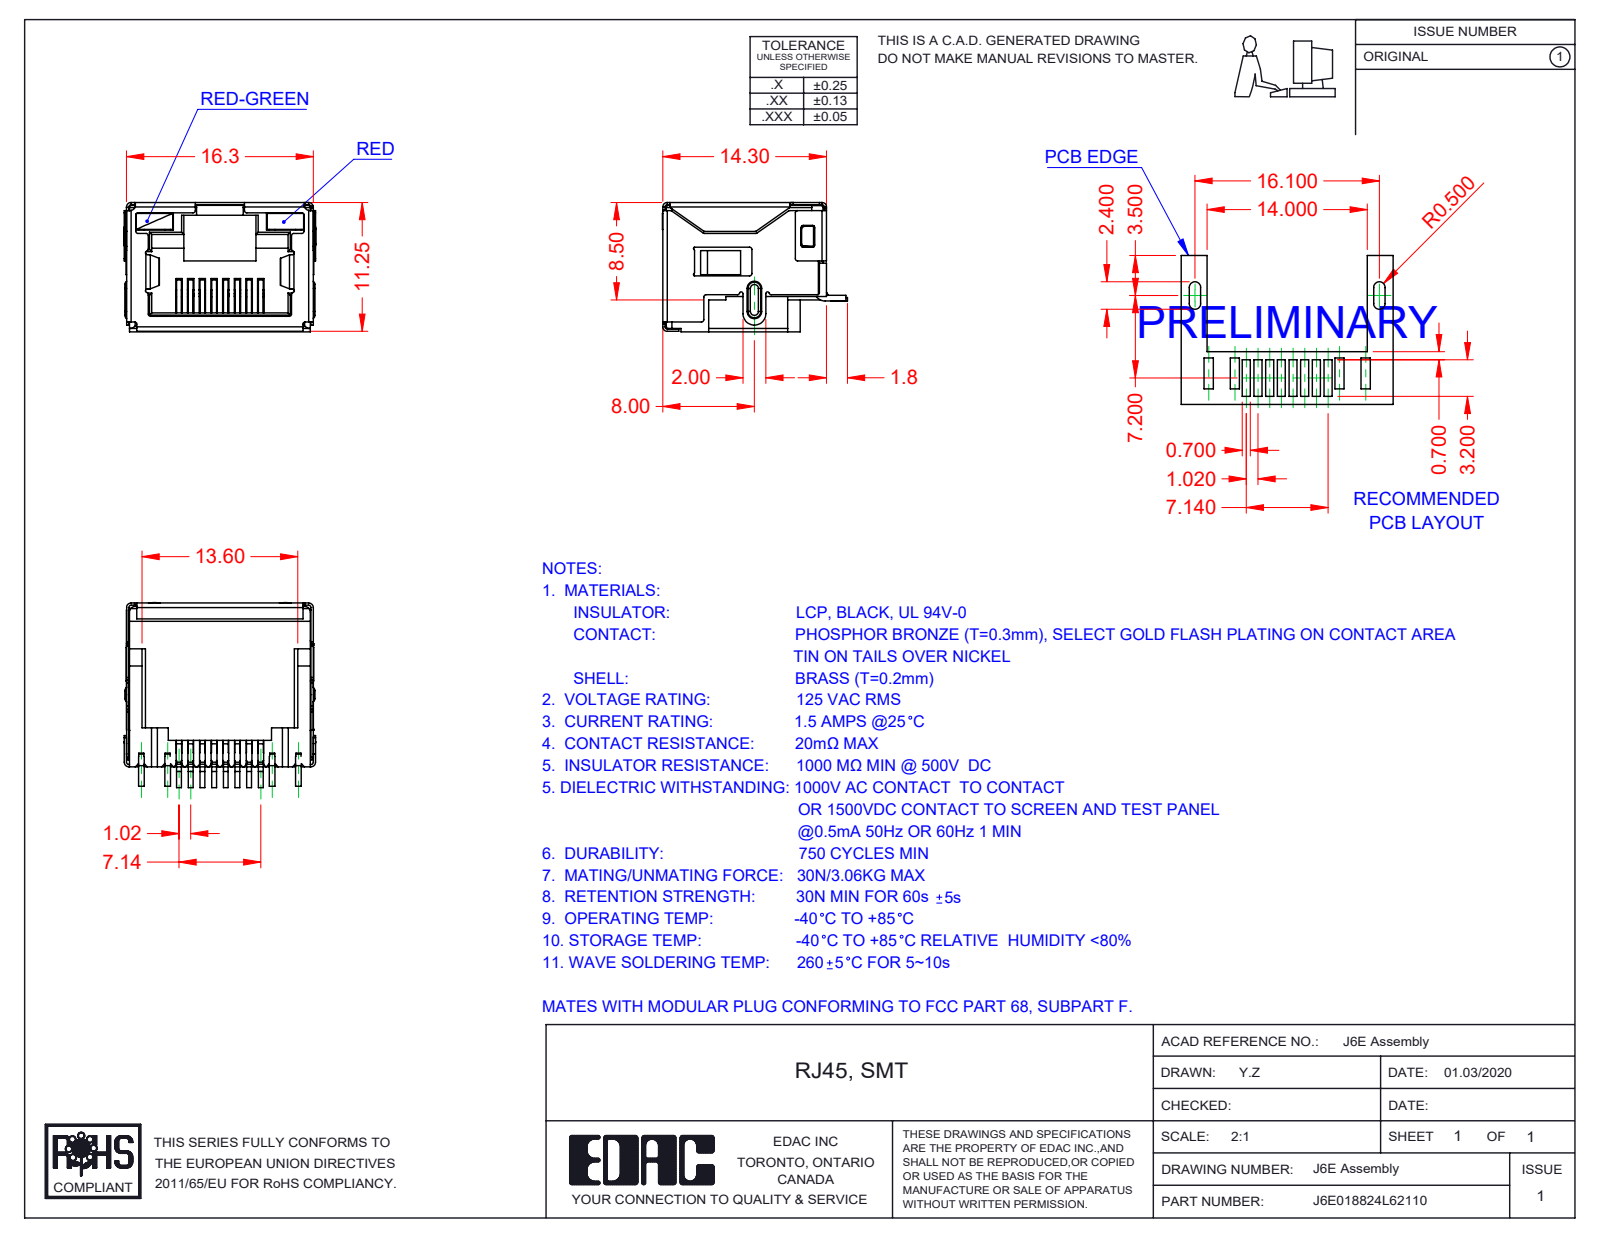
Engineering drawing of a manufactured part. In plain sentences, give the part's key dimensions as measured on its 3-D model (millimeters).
The part is named "6E Shield_LED; J6E018824L62110; 6E Contacts; 6E Insulator_LED (+2 more)". Its 3-D file was written by "SolidWorks 2016 (CONFIG_CONTROL_DESIGN)". It is 12 solids with 1498 faces: 1099 planar, 349 cylindrical and 50 other. Overall it measures 16.75 by 16.15 by 11.3 millimeters. Its volume is 1 109 cubic millimeters and its surface area 4 045 square millimeters. Partial cylindrical surfaces (rounded edges, fillets, slot ends): 82 of radius 0.2, 17 of radius 0.25, 13 of radius 0.4, 13 of radius 0.5, 10 of radius 0.1, 7 of radius 0.15, 4 of radius 0.3, 3 of radius 1. The main face-to-face distances are 11.05, 16.05, 16.1, 15.85, 11.1, 11.3, 2.4, 0.7, 9.85, 0.49.
